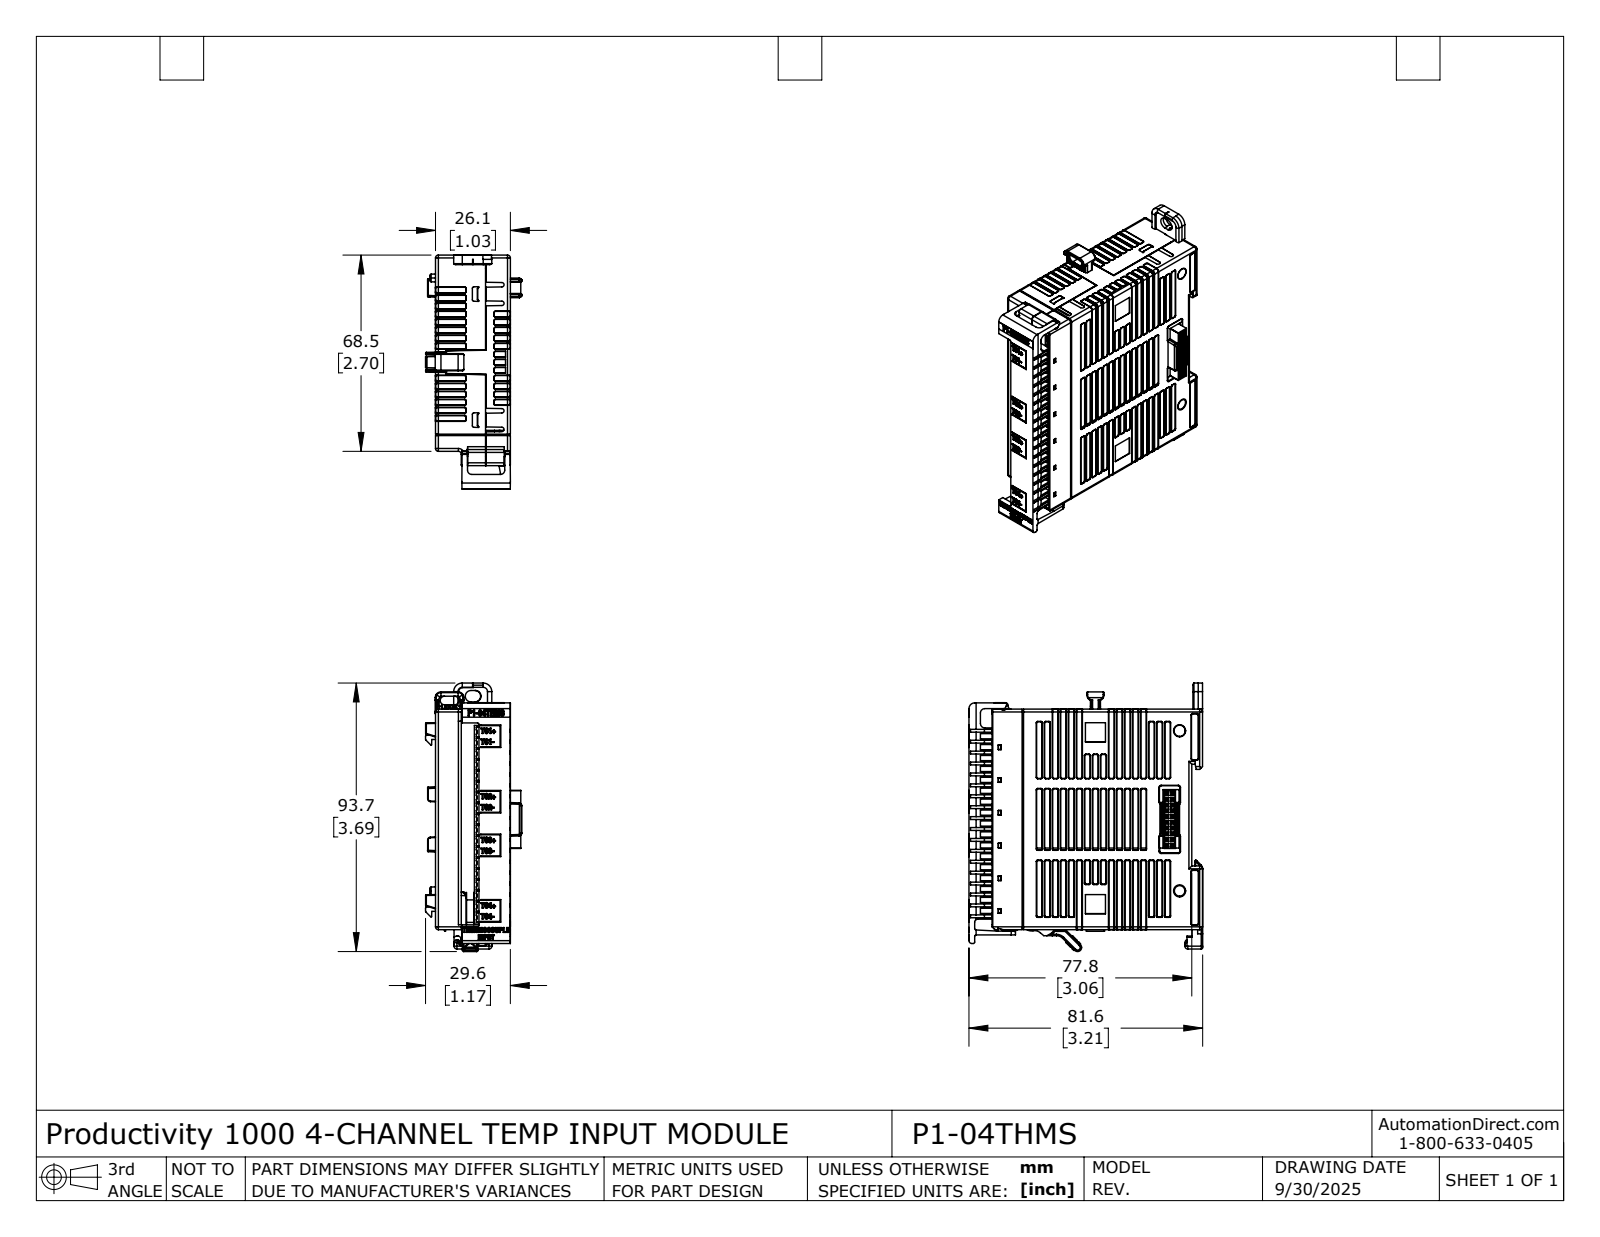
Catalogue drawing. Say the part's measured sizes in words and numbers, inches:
The part is named "P1-04THMS". Its 3-D file was written by "SolidWorks 2024 (AUTOMOTIVE_DESIGN)". It is 25 solids with 5604 faces: 2946 planar, 1352 cylindrical and 1306 other. Overall it measures 3.69 by 3.214 by 1.324 inches. Its volume is 2.905 cubic inches and its surface area 72.89 square inches. Round holes: 20 of diameter 0.01, 8 of diameter 0.024, 1 of diameter 0.049, 1 of diameter 0.069. Round bosses or shafts: 1 of diameter 0.064. Partial cylindrical surfaces (rounded edges, fillets, slot ends): 254 of radius 0.01, 120 of radius 0.02, 111 of radius 0.012, 84 of radius 0.008, 75 of radius 0.039, 18 of radius 0.062, 14 of radius 0.079, 11 of radius 0.059. The main face-to-face distances are 0.06, 0.97, 0.91, 1.03, 2.972, 0.059, 1.029, 0.969, 0.96, 1.8. The hole center spacings are 0.079, 0.111, 0.157, 0.176, 0.236, 0.249, 0.315, 0.325.
